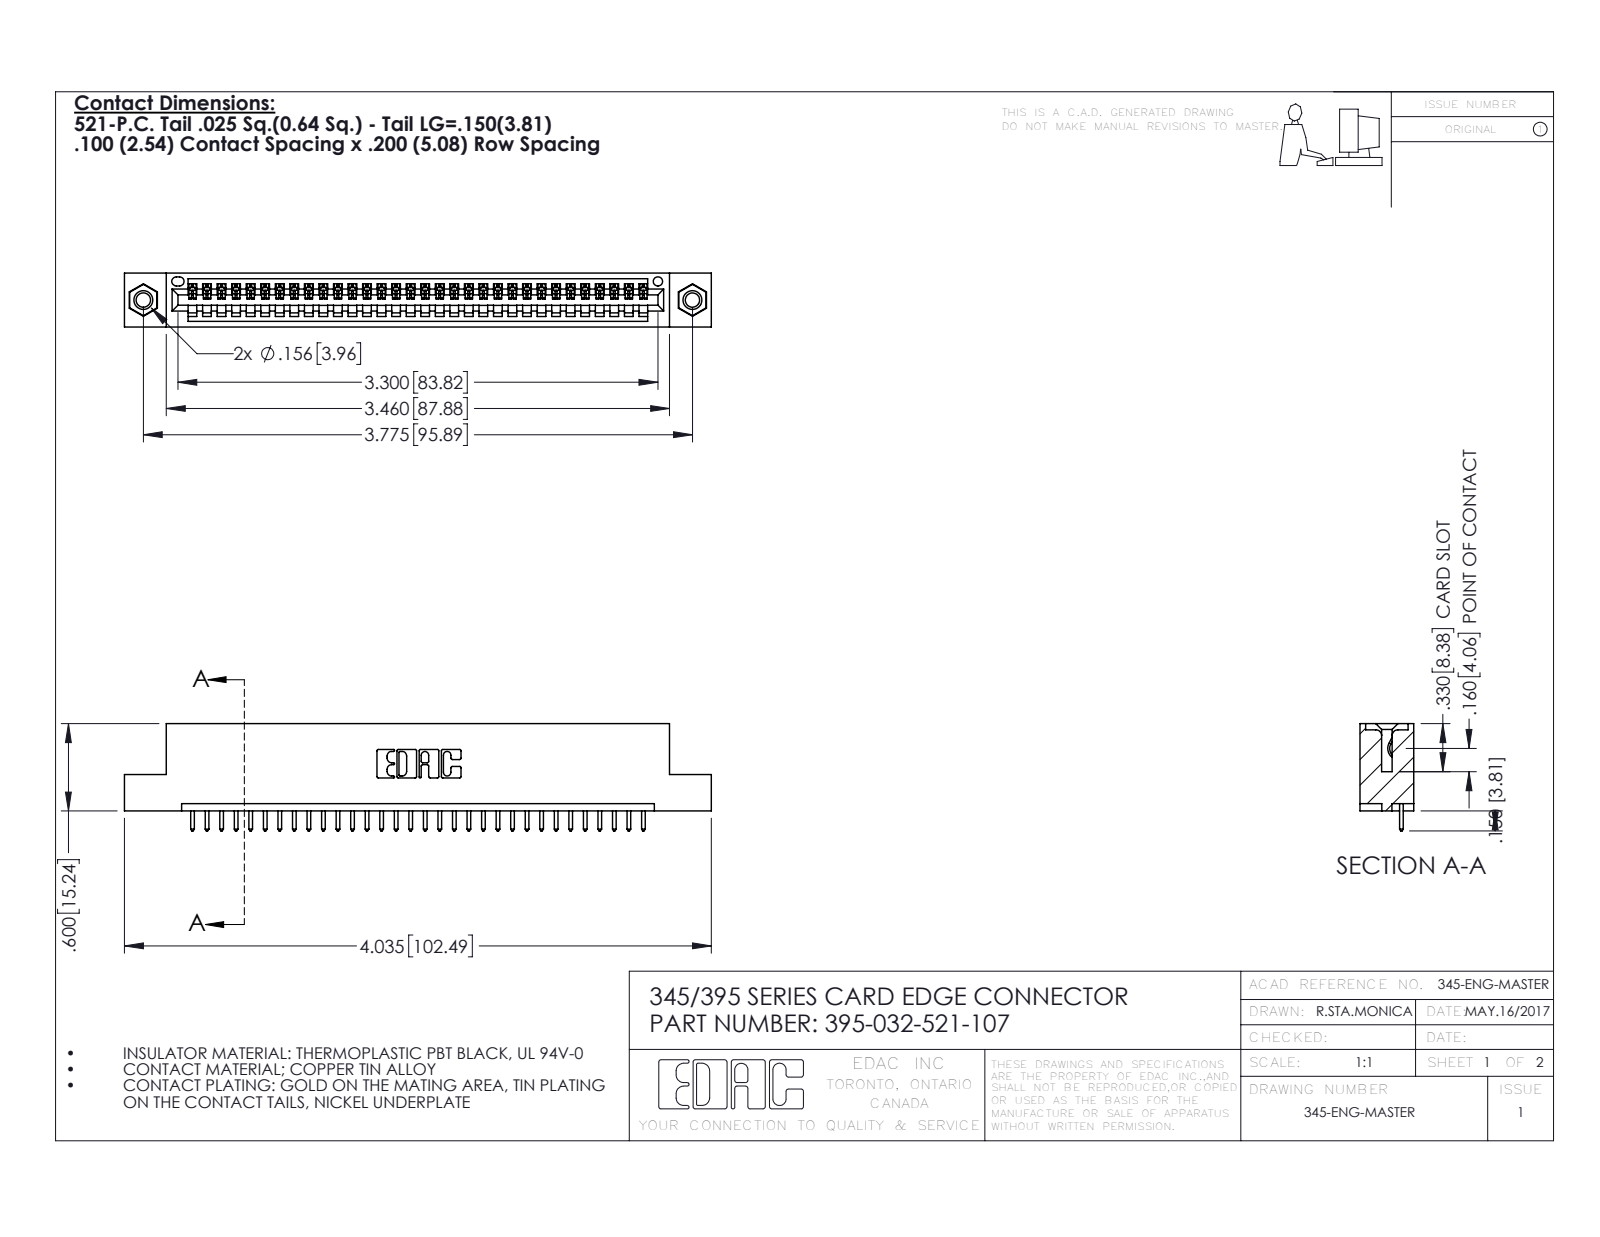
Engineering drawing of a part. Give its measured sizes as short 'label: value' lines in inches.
name: 345-292-001_345-293-121; 395-032-521-107; 345 Part_Flush Mounting Lugs - 0.156 Dia-TI; 345-250-001_345-250-005-103
written by: SolidWorks 2016 (CONFIG_CONTROL_DESIGN)
unit: in
bodies: 35 solids, 2042 faces (1392 planar, 634 cylindrical, 16 other)
size: 4.035 × 0.737 × 0.37
volume: 0.583 in³; area: 18.96 in²
holes: 2× ⌀0.098, 2× ⌀0.125, 2× ⌀0.156, 1× ⌀0.064
bosses: 2× ⌀0.155
rounds: 64× R0.006, 64× R0.01, 22× R0.01, 6× R0.007, 6× R0.031, 3× R0.026, 2× R0.031, 2× R0.04
face distances: 0.072, 0.298, 0.2, 0.37, 0.098, 0.272, 0.025, 0.225, 0.149, 0.072
hole spacings: 0.27, 3.54, 3.775
